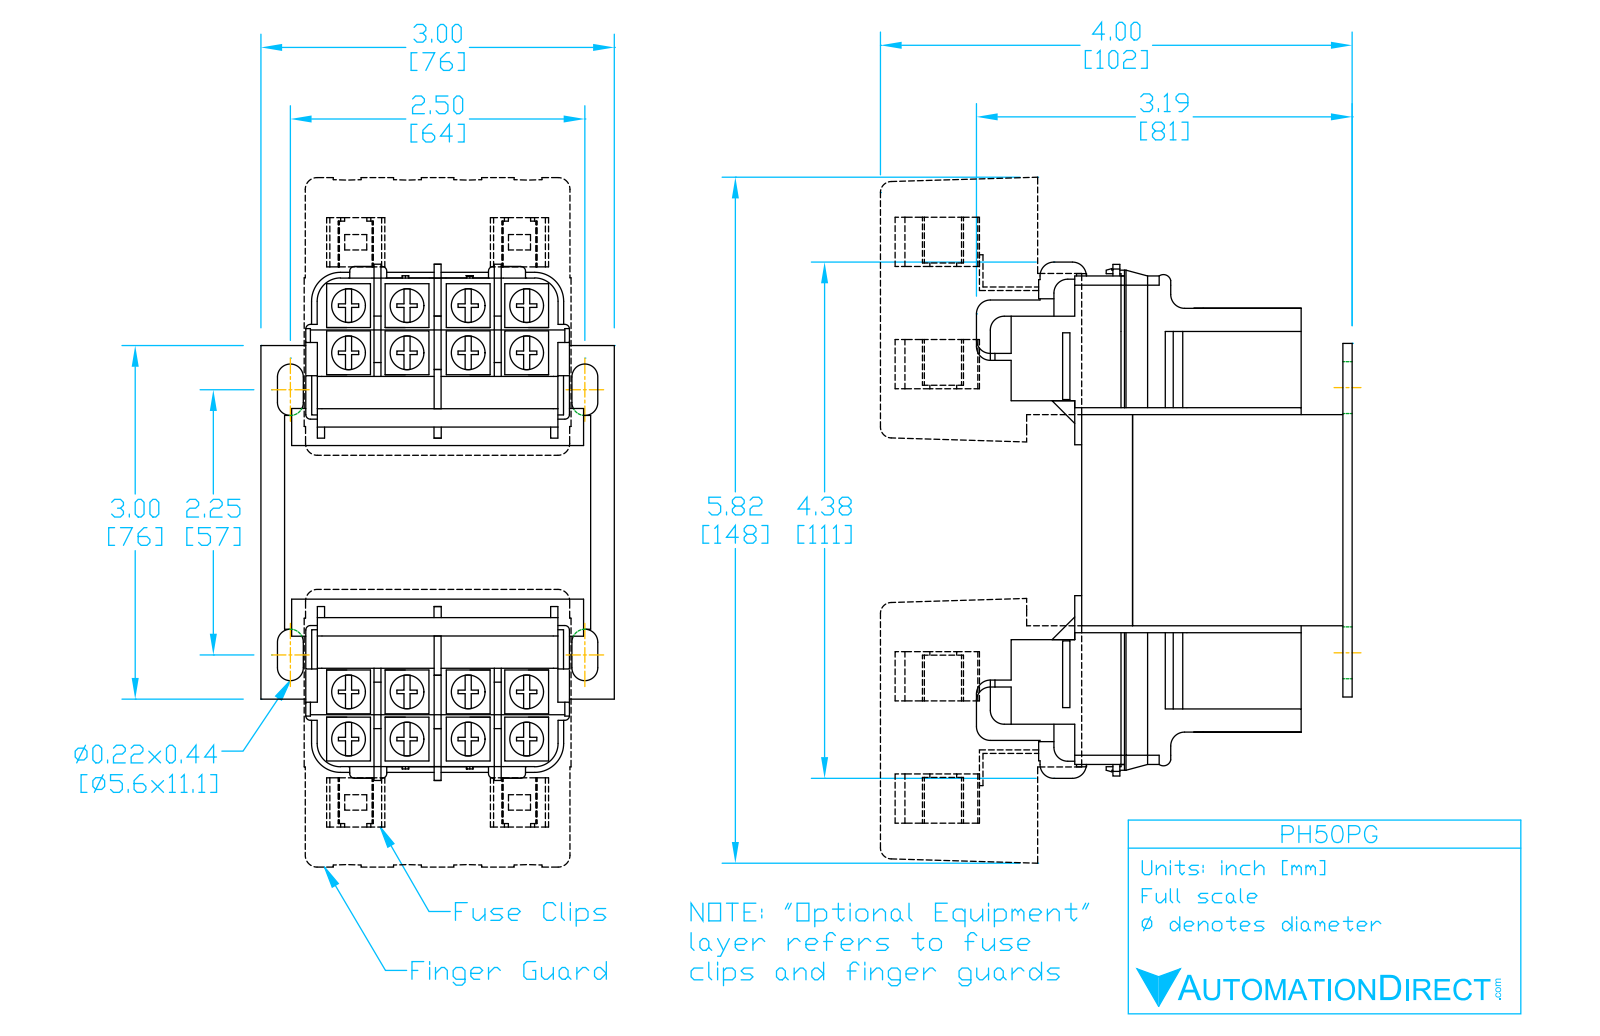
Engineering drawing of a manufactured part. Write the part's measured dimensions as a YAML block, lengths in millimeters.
part_name: "PH50PG"
step_written_by: "SolidWorks 2017 (AUTOMOTIVE_DESIGN)"
units: millimeters
bodies: {solids: 8, faces: 476, planar: 296, cylindrical: 126, other: 54}
overall_size: [108, 79.8, 76.2]
volume: 332700
surface_area: 65420
round_holes:
  - {diameter: 4, count: 4}
partial_cylinders:
  - {radius: 1, count: 48}
  - {radius: 2.8, count: 8}
  - {radius: 3, count: 8}
  - {radius: 5, count: 8}
  - {radius: 2.5, count: 6}
  - {radius: 6.2, count: 4}
  - {radius: 8.1, count: 2}
face_to_face_distances: [42, 1.8, 1.5, 44, 45.7, 11, 55, 9.2, 7, 59]
hole_center_spacings: [23.2, 58.8, 63.2]
